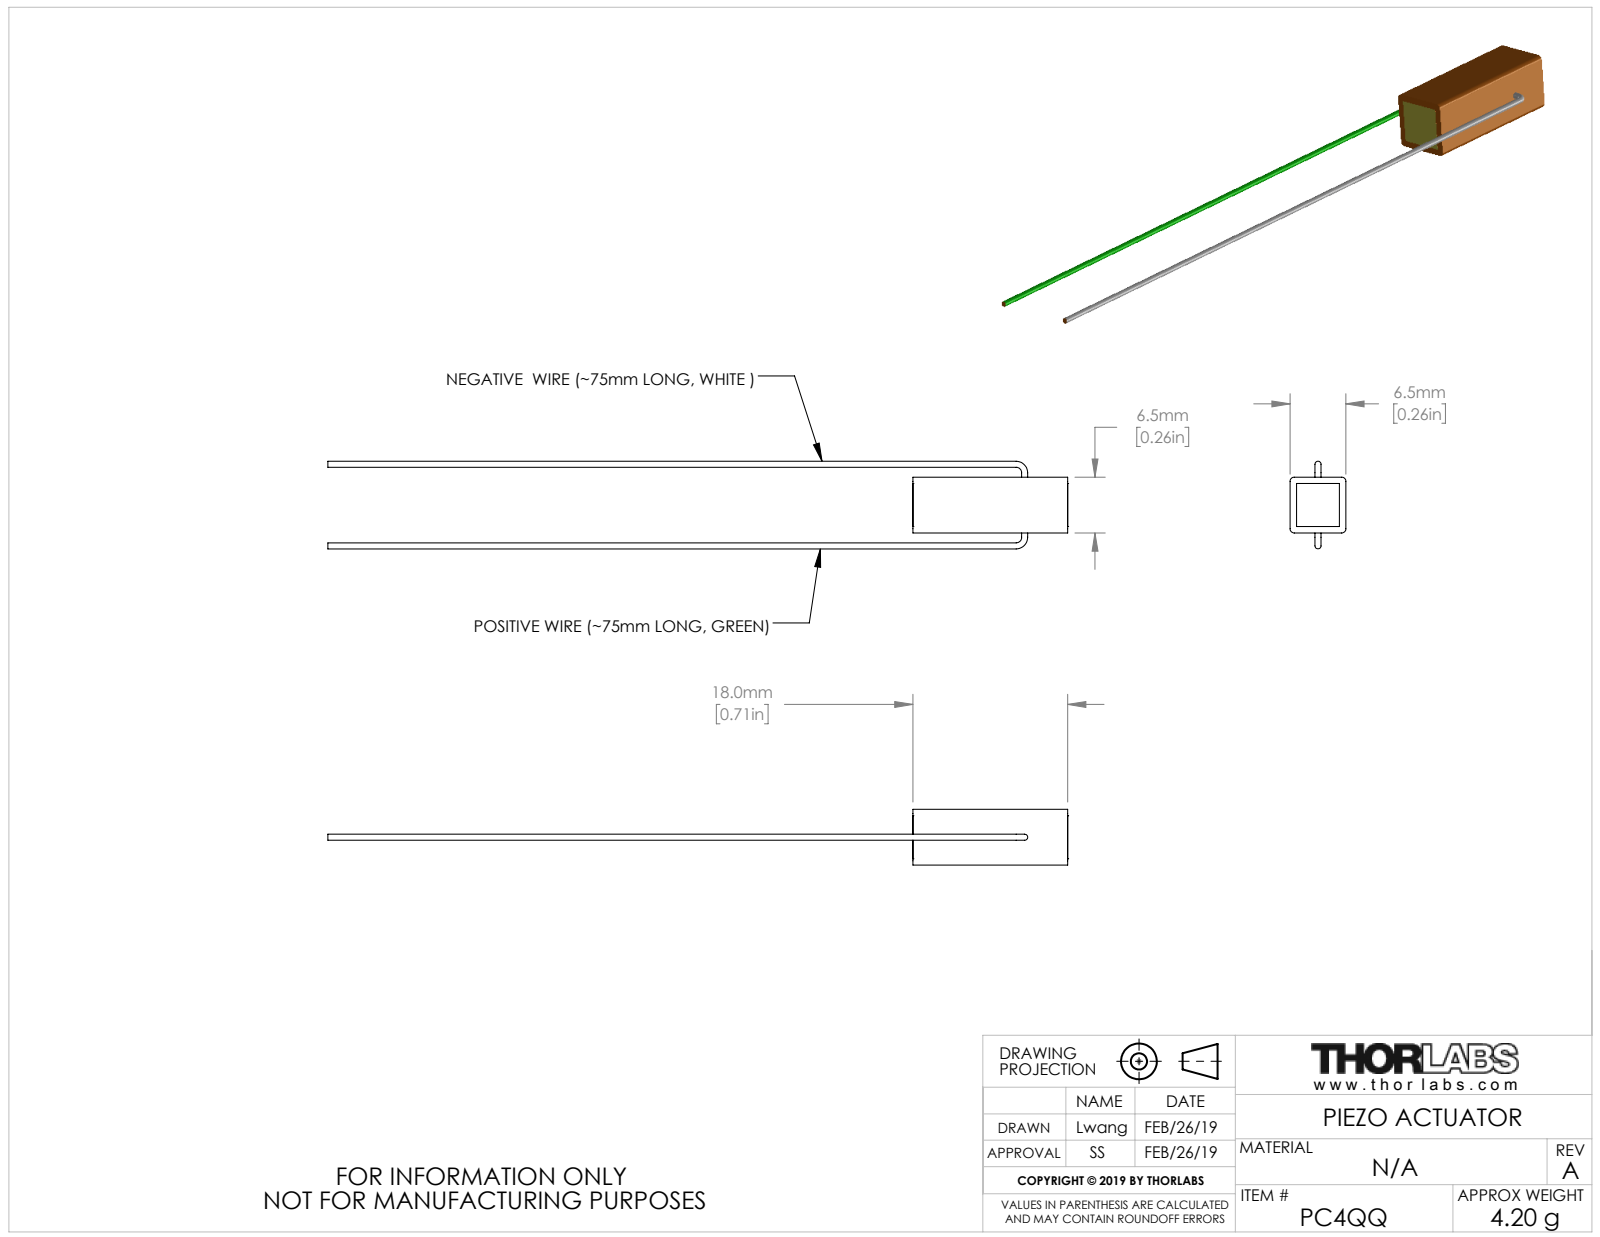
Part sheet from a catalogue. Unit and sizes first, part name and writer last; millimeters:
Units: millimetres
Overall size (bounding box): 86.13 × 10.2 × 6.5
Round bosses / shafts (diameter × count): ⌀0.7 ×3
Partial cylindrical surfaces — rounded edges, fillets, slot ends (radius × count): R0.5 ×4
Main face-to-face distances: 6.5, 18.01, 18.02, 18, 68.11, 68.12, 86.12, 86.13, 5.75, 0.75
Volume: 820 mm³ · Surface area: 898 mm²
Bodies: 1 solid, 34 faces (18 planar, 12 cylindrical, 4 other)
Part name (STEP PRODUCT): CTN013823
STEP written by: SolidWorks 2018 (AUTOMOTIVE_DESIGN)
